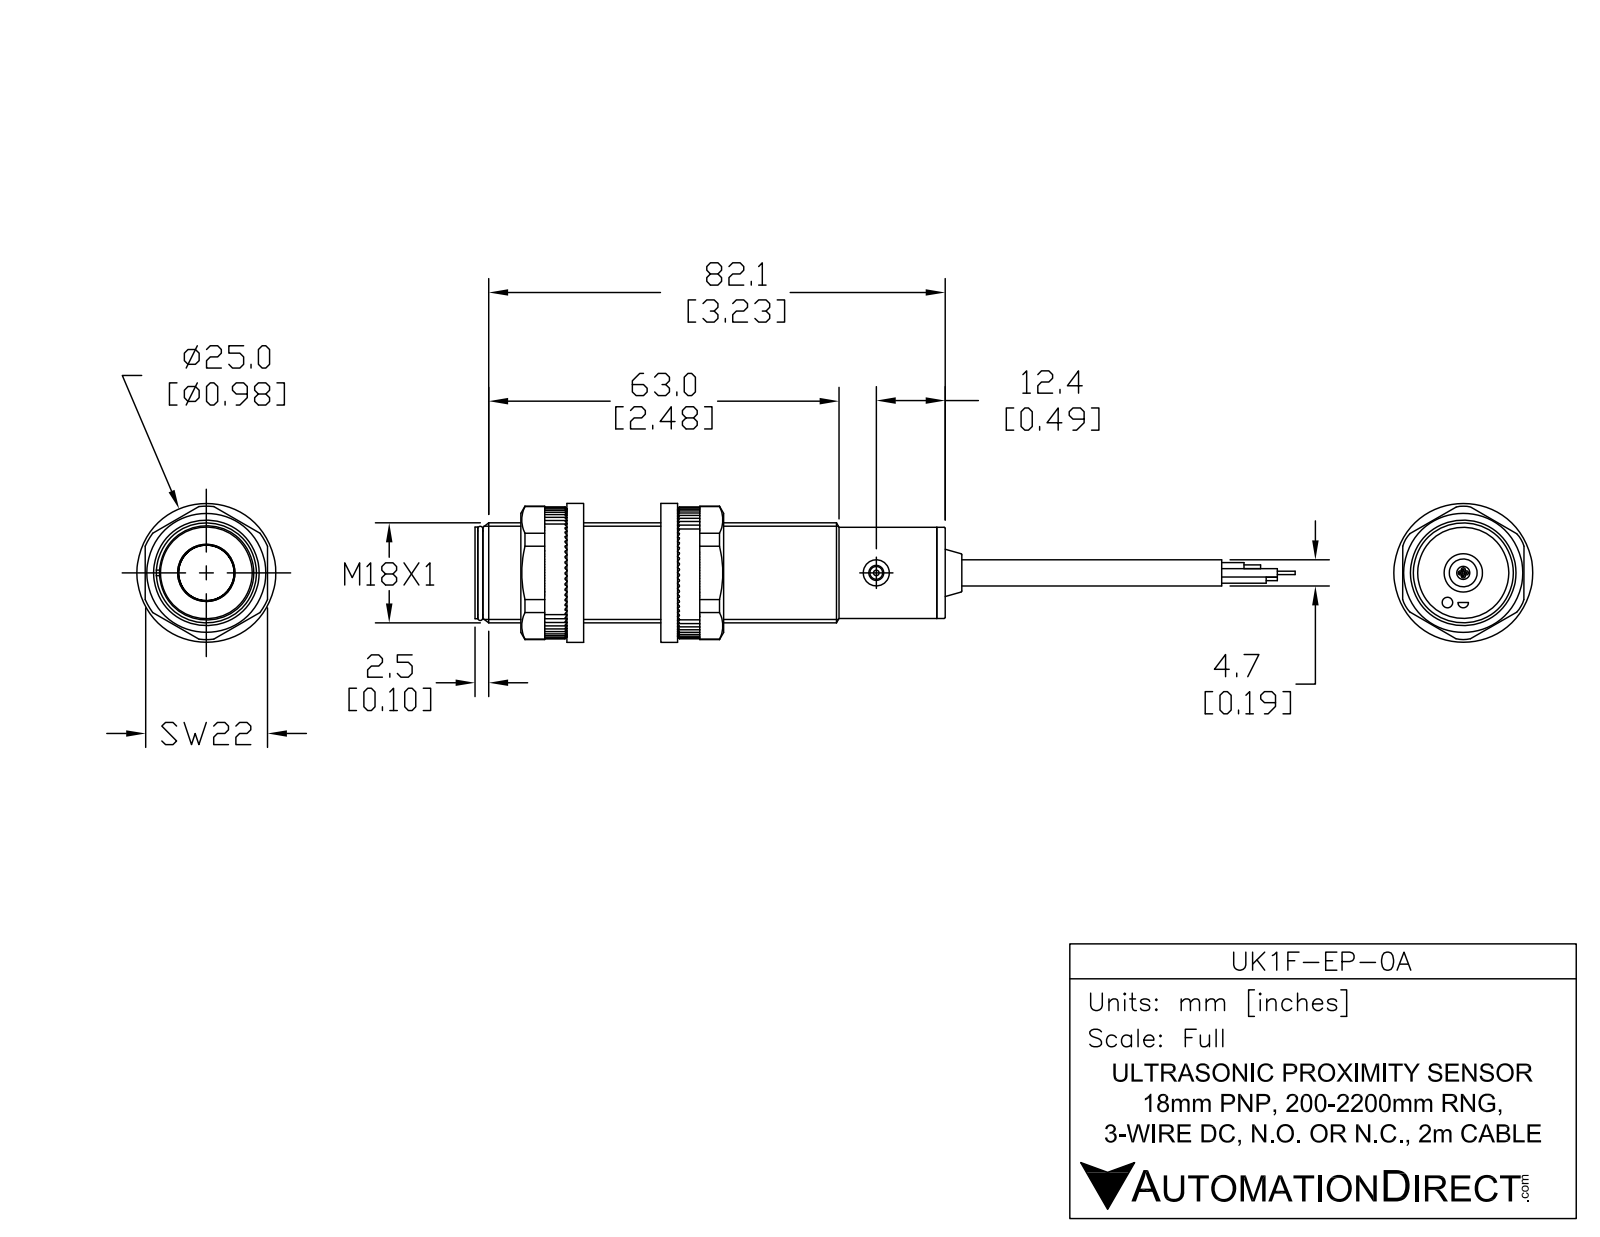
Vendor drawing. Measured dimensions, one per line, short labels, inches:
name: UK1F-EP-0A
written by: SolidWorks 2017 (AUTOMOTIVE_DESIGN)
unit: in
bodies: 6 solids, 55 faces (17 planar, 24 cylindrical, 14 other)
size: 4.832 × 0.709 × 0.709
volume: 1.285 in³; area: 10.69 in²
holes: 2× ⌀0.185, 1× ⌀0.106
bosses: 1× ⌀0.709, 1× ⌀0.646, 1× ⌀0.622, 1× ⌀0.374, 1× ⌀0.189, 1× ⌀0.091
face distances: 3.193, 3.252, 0.059, 0.039, 3.232, 3.291, 0.041, 3.234, 3.293, 3.257
